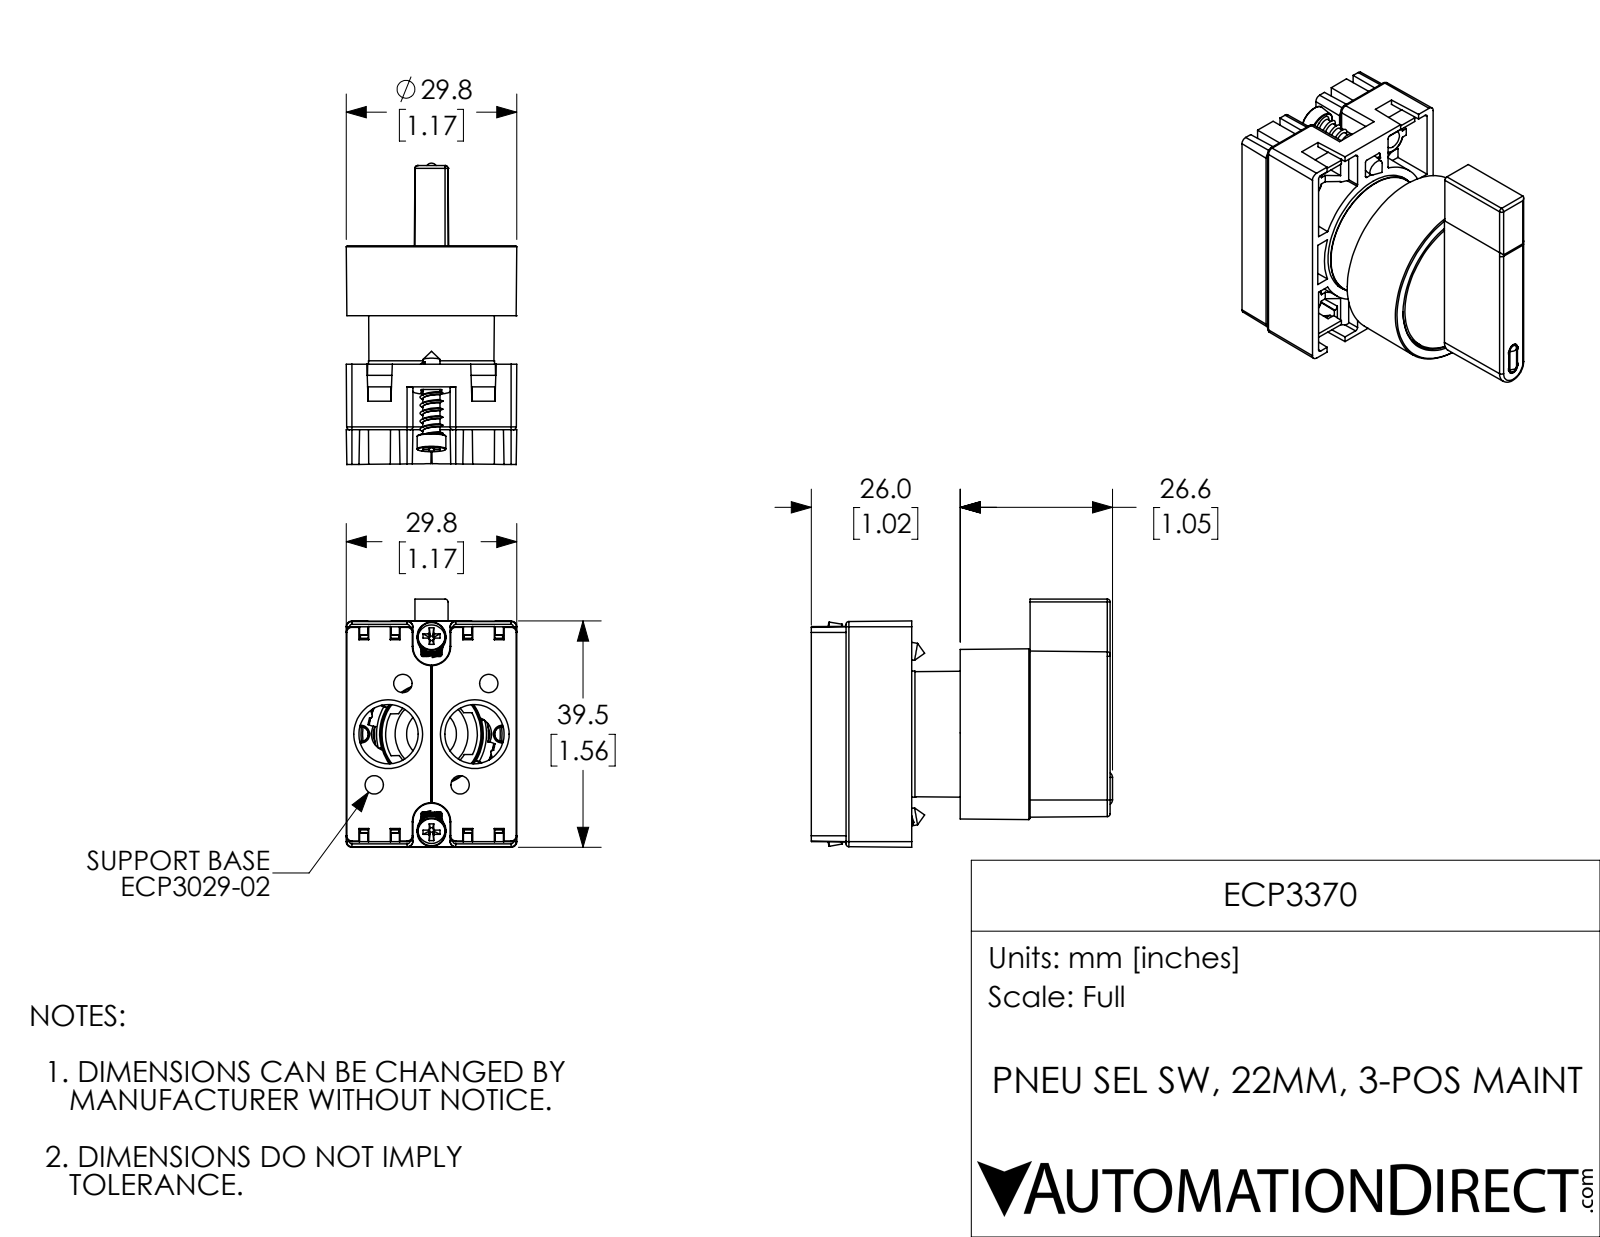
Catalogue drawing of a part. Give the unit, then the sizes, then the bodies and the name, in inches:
Units: inches
Overall size (bounding box): 2.071 × 1.706 × 1.173
Round holes (diameter × count): ⌀0.081 ×4, ⌀0.407 ×2, ⌀0.5 ×1, ⌀0.551 ×1, ⌀0.697 ×1, ⌀0.75 ×1, ⌀0.756 ×1, ⌀0.854 ×1, ⌀0.976 ×1, ⌀1.024 ×1
Round bosses / shafts (diameter × count): ⌀0.197 ×2, ⌀0.118 ×2, ⌀1.004 ×1, ⌀0.866 ×1, ⌀0.85 ×1, ⌀0.669 ×1, ⌀0.343 ×1
Partial cylindrical surfaces — rounded edges, fillets, slot ends (radius × count): R0.02 ×23, R0.012 ×10, R0.039 ×9, R0.006 ×8, R0.008 ×4, R0.008 ×2, R0.118 ×2, R0.128 ×2
Main face-to-face distances: 1.265, 0.059, 0.067, 0.712, 0.743, 0.299, 0.712, 0.715, 0.814, 0.451
Hole centre spacings: 0.304, 0.541, 0.817, 0.295, 0.472, 0.972, 1.081, 0.591
Volume: 1.144 in³ · Surface area: 32.38 in²
Bodies: 9 solids, 850 faces (410 planar, 161 cylindrical, 279 other)
Part name (STEP PRODUCT): ECP3370
STEP written by: SolidWorks 2017 (AUTOMOTIVE_DESIGN)
